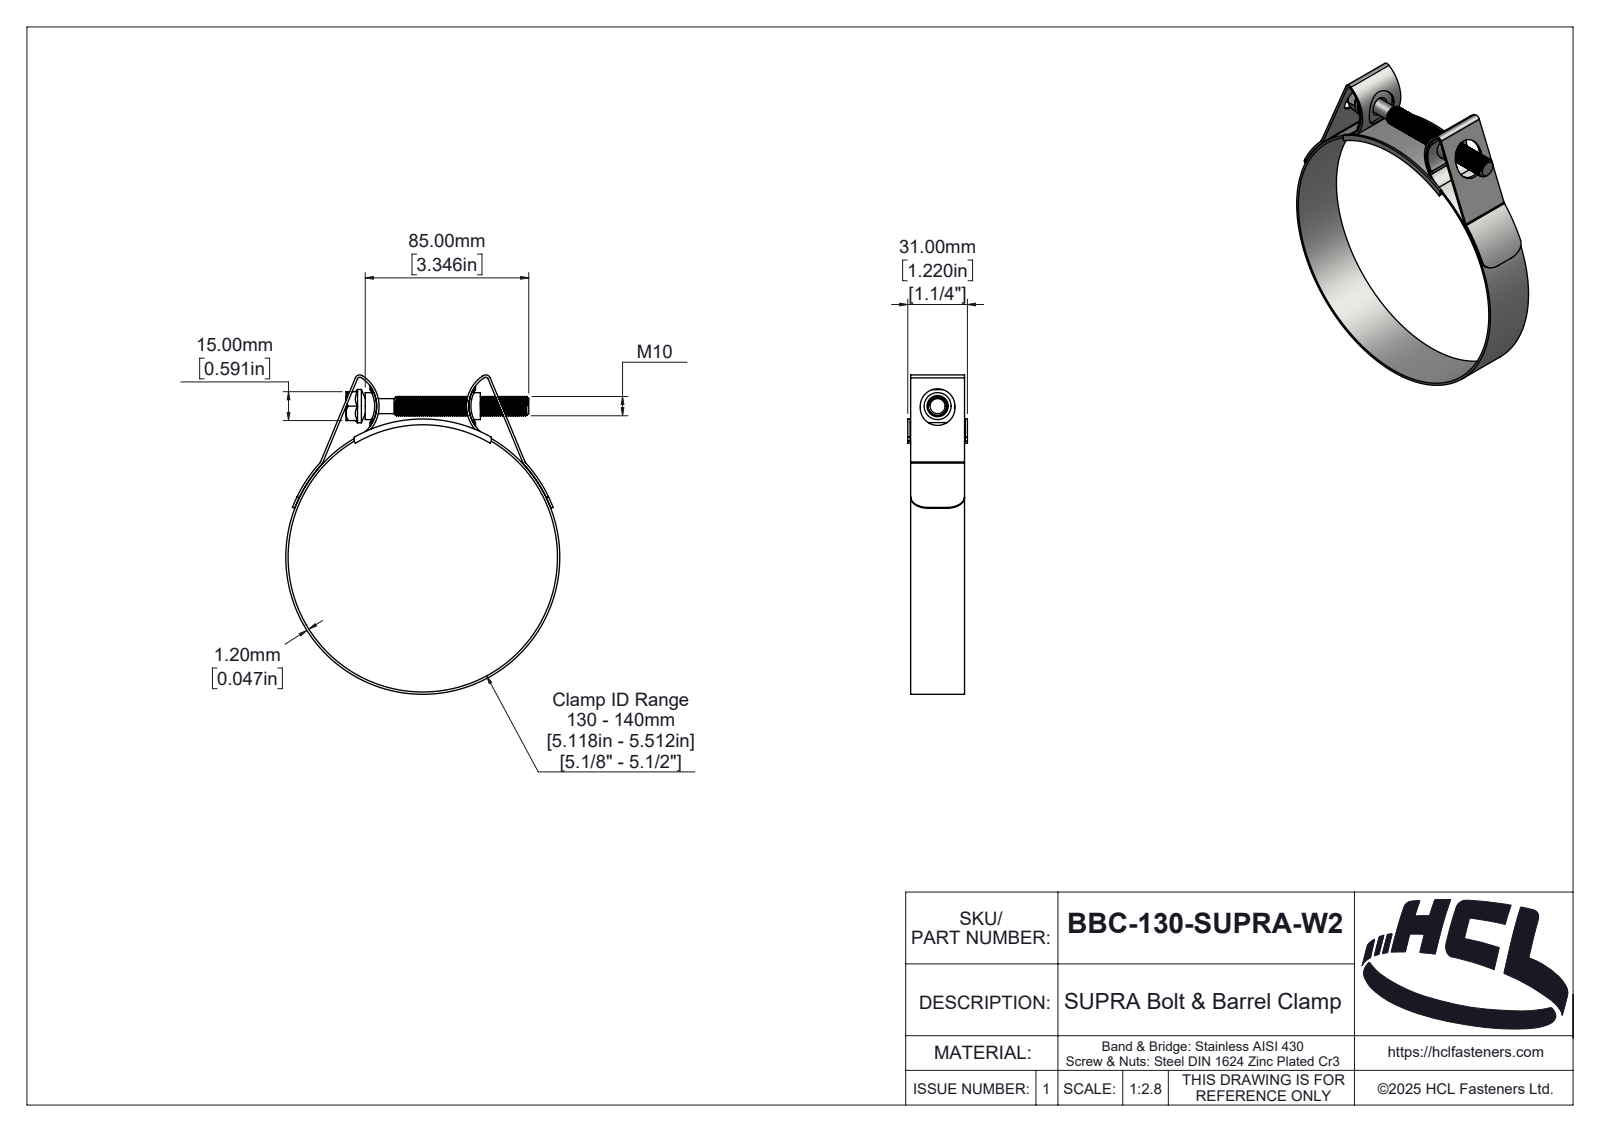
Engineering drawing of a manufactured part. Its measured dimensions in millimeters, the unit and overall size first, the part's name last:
Units: millimetres
Overall size (bounding box): 165.9 × 142.4 × 31
Round holes (diameter × count): ⌀140 ×1
Round bosses / shafts (diameter × count): ⌀142.4 ×1, ⌀17.32 ×1, ⌀14 ×1, ⌀10 ×1, ⌀7.8 ×1
Partial cylindrical surfaces — rounded edges, fillets, slot ends (radius × count): R1 ×4, R1.3 ×2, R2 ×2, R2.5 ×2, R3.2 ×2, R9 ×2, R16.49 ×2, R17.49 ×2
Main face-to-face distances: 1.2, 28, 1.5, 29.5, 29.8, 28.3, 31, 28.6, 15, 2.5
Volume: 31 247 mm³ · Surface area: 46 325 mm²
Bodies: 5 solids, 382 faces (46 planar, 249 cylindrical, 87 other)
Part name (STEP PRODUCT): BBC-130-SUPRA-W2
STEP written by: SolidWorks 2025 (AUTOMOTIVE_DESIGN)
